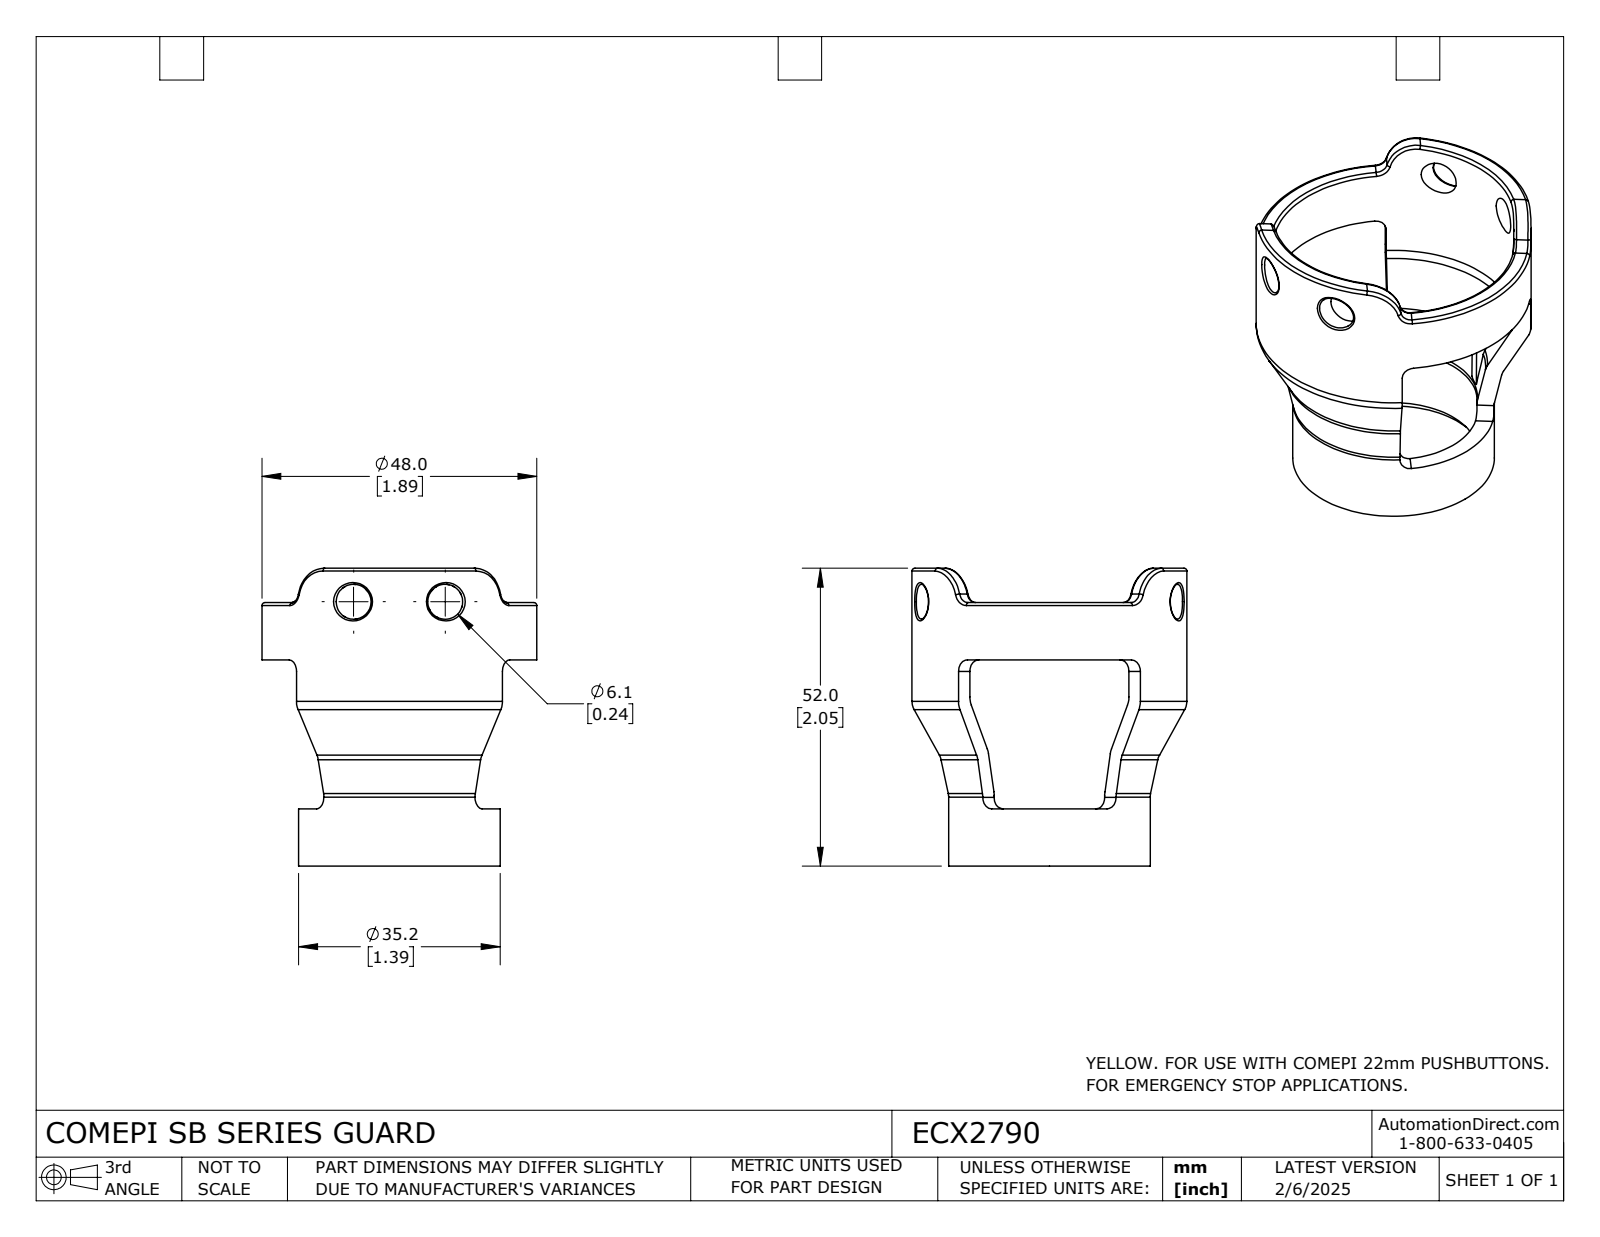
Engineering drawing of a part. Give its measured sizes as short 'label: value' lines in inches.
name: ECX2790
written by: SolidWorks 2024 (CONFIG_CONTROL_DESIGN)
unit: in
bodies: 1 solid, 114 faces (22 planar, 34 cylindrical, 58 other)
size: 2.047 × 1.89 × 1.89
volume: 0.825 in³; area: 16.62 in²
holes: 2× ⌀0.24, 1× ⌀1.15, 1× ⌀1.24, 1× ⌀1.654
bosses: 1× ⌀1.89, 1× ⌀1.386
rounds: 12× R0.079, 4× R0.236
face distances: 1.417, 0.394, 1.811, 1.024, 0.059, 0.335, 1.358, 1.752, 2.047, 1.988
hole spacings: 0.63
